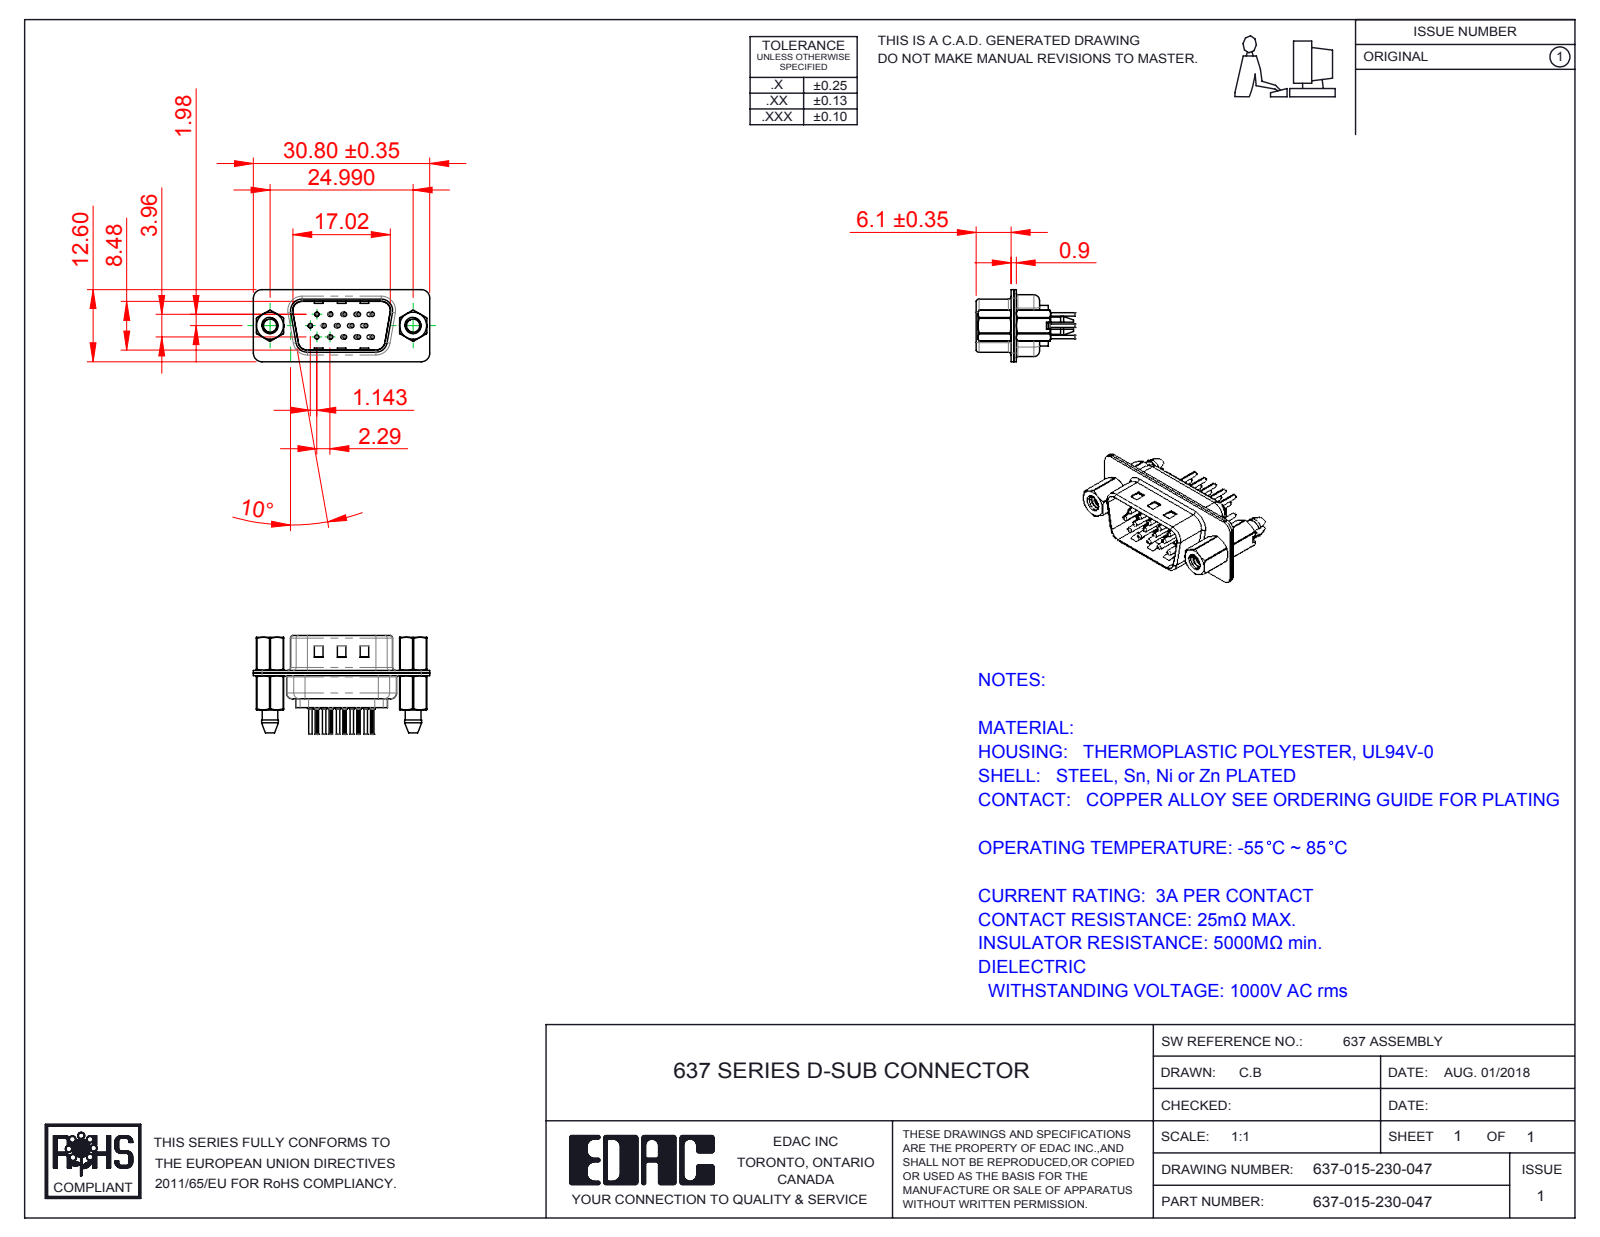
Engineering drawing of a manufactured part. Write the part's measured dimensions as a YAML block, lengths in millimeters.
part_name: "637-015-230-047; 637 4-40 Threaded Boardlock_LP; 637 4-40 Hex Standoff; 637 Contact Row 3_30 (+5 more)"
step_written_by: "SolidWorks 2016 (CONFIG_CONTROL_DESIGN)"
units: millimeters
bodies: {solids: 22, faces: 2004, planar: 521, cylindrical: 788, other: 695}
overall_size: [30.8, 17.25, 12.6]
volume: 1642
surface_area: 5415
round_holes:
  - {diameter: 1.6, count: 27}
  - {diameter: 0.2, count: 15}
  - {diameter: 0.35, count: 15}
  - {diameter: 1.1, count: 15}
  - {diameter: 0.75, count: 12}
  - {diameter: 2, count: 12}
  - {diameter: 2.26, count: 2}
  - {diameter: 2.29, count: 2}
  - {diameter: 4, count: 2}
  - {diameter: 4.8, count: 2}
round_bosses_or_shafts:
  - {diameter: 2, count: 15}
  - {diameter: 1.5, count: 15}
  - {diameter: 0.75, count: 15}
  - {diameter: 0.6, count: 15}
  - {diameter: 4.9, count: 2}
  - {diameter: 2.79, count: 2}
partial_cylinders:
  - {radius: 0.1, count: 30}
  - {radius: 1.5, count: 18}
  - {radius: 2, count: 12}
  - {radius: 0.5, count: 8}
  - {radius: 1.6, count: 6}
  - {radius: 0.25, count: 4}
  - {radius: 0.55, count: 4}
  - {radius: 0.7, count: 4}
face_to_face_distances: [0.45, 0.4, 0.9, 8.48, 0.7, 4.76, 8.88, 6.5, 4.55, 0.31]
hole_center_spacings: [3.96, 2.29, 2.28, 4.57, 2.42, 6.05, 4.84, 2.35]
